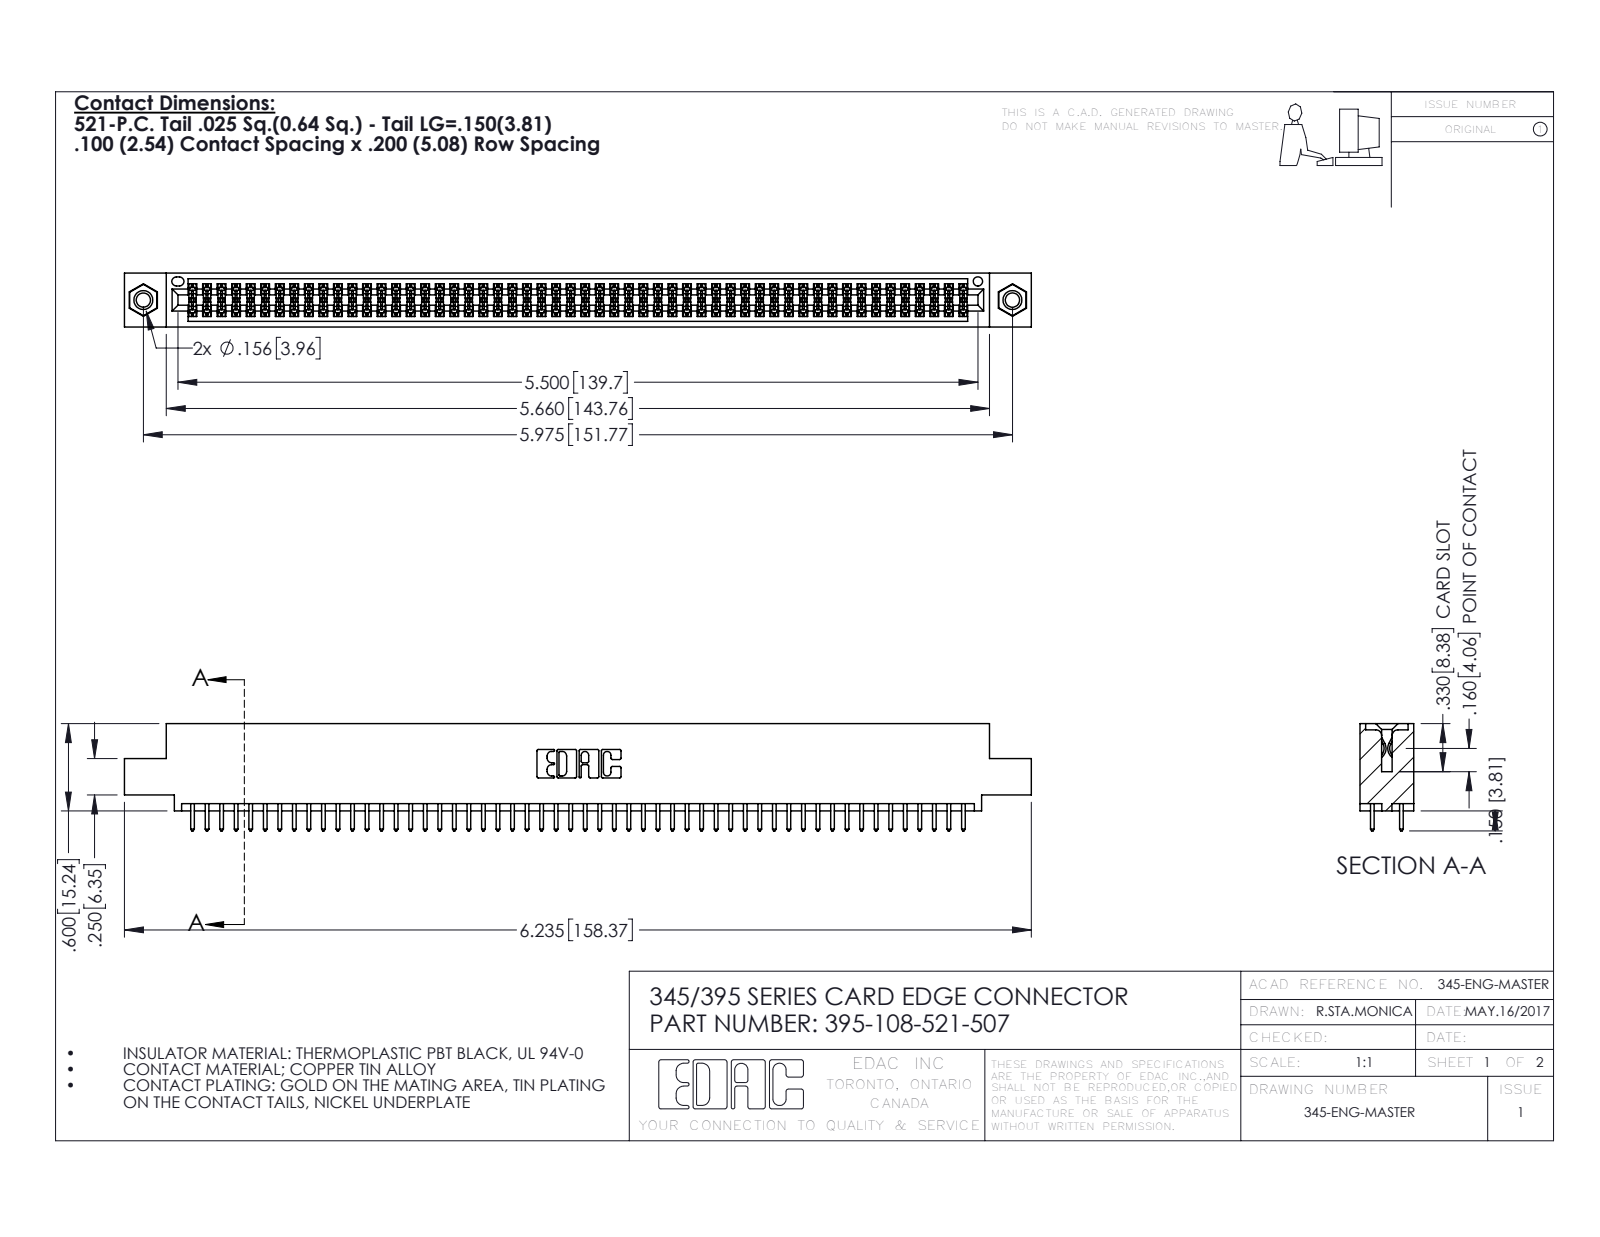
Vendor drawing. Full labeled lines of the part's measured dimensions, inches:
Part name (STEP PRODUCT): 395-108-521-507; 345-292-001_345-293-121; 345-250-001_345-250-005-103; 345 Part_0.110 Offset - 0.156 Dia-TI
STEP written by: SolidWorks 2016 (CONFIG_CONTROL_DESIGN)
Units: inches
Bodies: 111 solids, 5590 faces (3680 planar, 1894 cylindrical, 16 other)
Overall size (bounding box): 6.235 × 0.737 × 0.37
Volume: 0.938 in³ · Surface area: 35.31 in²
Round holes (diameter × count): ⌀0.098 ×2, ⌀0.125 ×2, ⌀0.156 ×2, ⌀0.064 ×1
Round bosses / shafts (diameter × count): ⌀0.155 ×2
Partial cylindrical surfaces — rounded edges, fillets, slot ends (radius × count): R0.006 ×162, R0.01 ×108, R0.01 ×22, R0.007 ×6, R0.031 ×6, R0.026 ×3, R0.014 ×2, R0.019 ×2
Main face-to-face distances: 0.072, 0.298, 0.2, 0.098, 0.272, 0.025, 0.37, 0.225, 0.175, 0.149
Hole centre spacings: 0.27, 5.739, 5.975
